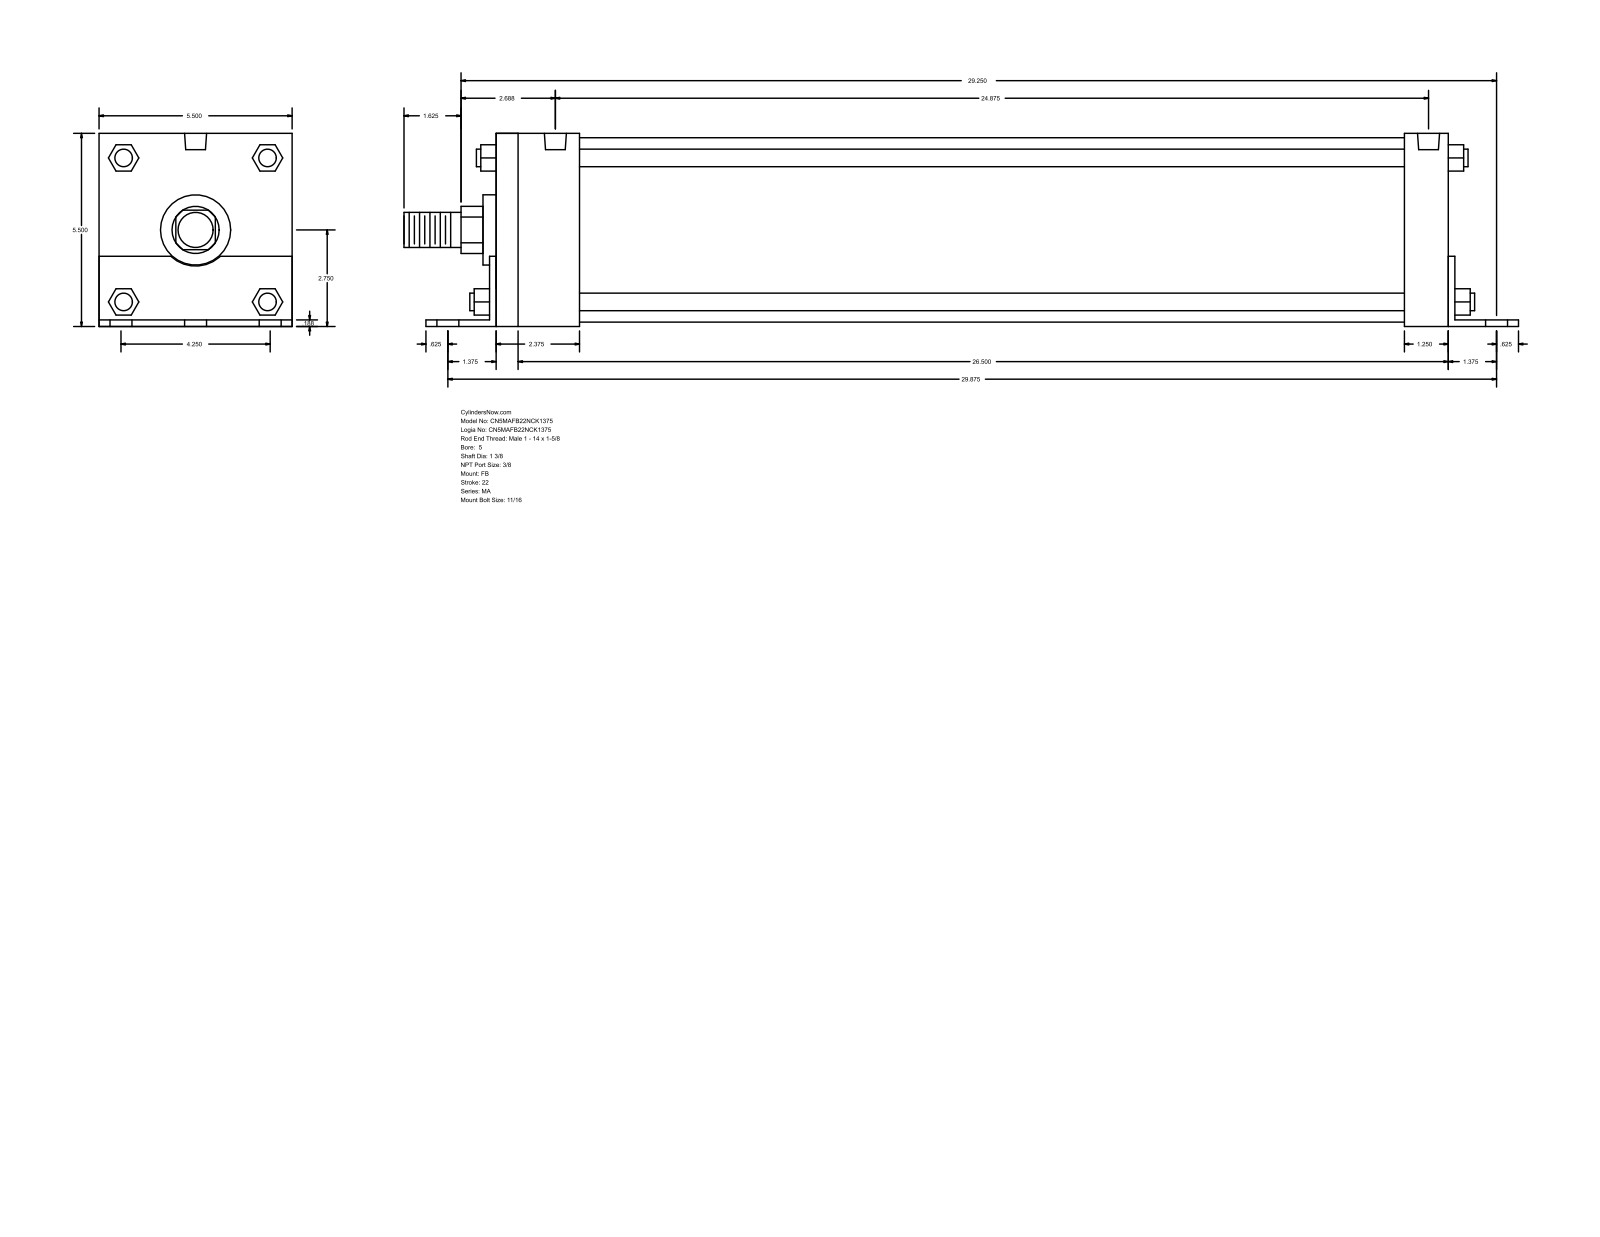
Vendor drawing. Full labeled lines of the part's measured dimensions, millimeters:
Part name (STEP PRODUCT): MA_FB__0500_1.375
STEP written by: GSSL Pune (CONFIG_CONTROL_DESIGN)
Units: millimetres
Bodies: 0 solids, 140 faces (105 planar, 35 cylindrical, 0 other)
Overall size (bounding box): 806.45 × 139.75 × 139.7
Round holes (diameter × count): ⌀17.46 ×6, ⌀11.11 ×4, ⌀15.93 ×2
Round bosses / shafts (diameter × count): ⌀12.7 ×4, ⌀133.35 ×1, ⌀50.8 ×1, ⌀34.92 ×1, ⌀25.4 ×1
Partial cylindrical surfaces — rounded edges, fillets, slot ends (radius × count): R17.06 ×1, R26.16 ×1
Main face-to-face distances: 139.7, 4.76, 139.75, 693.74, 4.71, 134.99, 688.98, 698.5, 65.08, 60.32
Hole centre spacings: 53.98, 760.75, 758.83, 73.04, 76.33, 94.68, 98.64, 107.96
